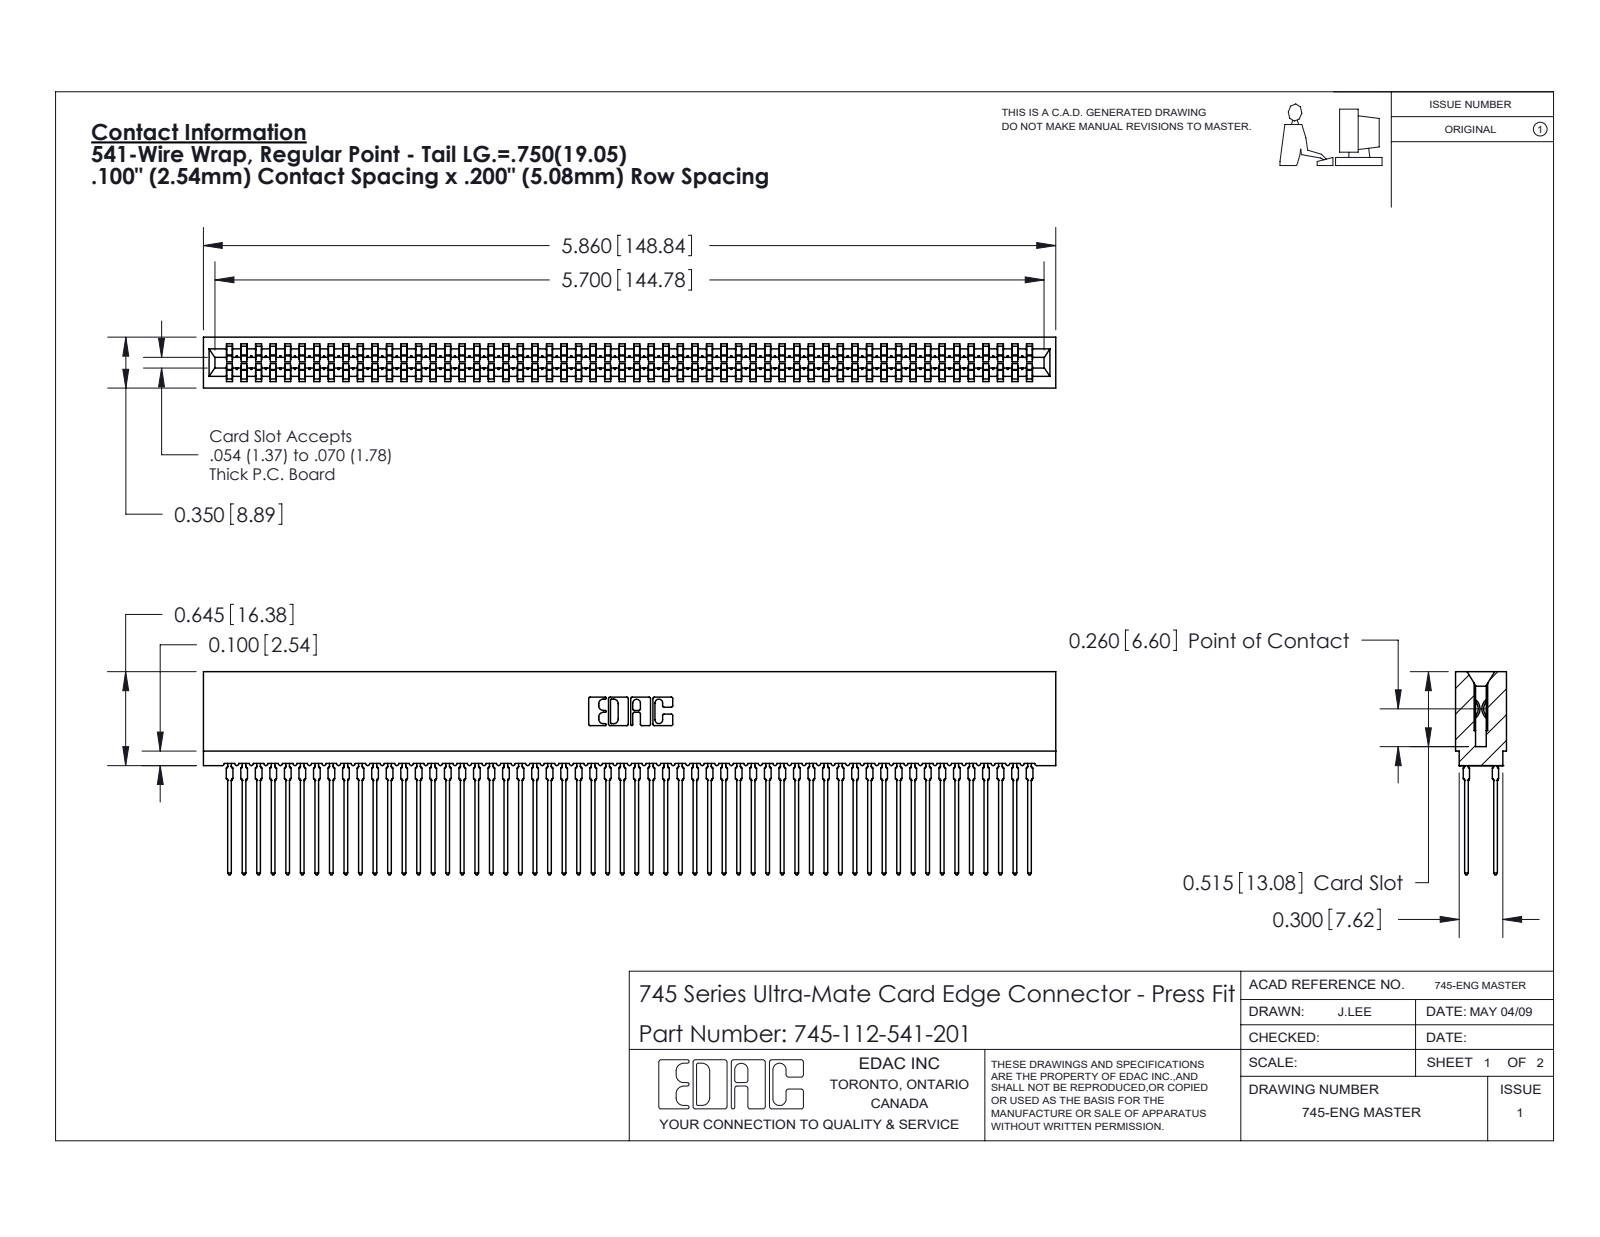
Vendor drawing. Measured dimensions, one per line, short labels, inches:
name: 745-112-541-201; 745-292-001_541; 745 Part_Insulator Option - 01
written by: SolidWorks 2020 (CONFIG_CONTROL_DESIGN)
unit: in
bodies: 113 solids, 10119 faces (5207 planar, 2000 cylindrical, 2912 other)
size: 5.86 × 1.396 × 0.35
volume: 0.846 in³; area: 47.65 in²
rounds: 224× R0.021, 112× R0.015, 22× R0.01, 8× R0.005, 8× R0.011, 6× R0.007, 6× R0.031, 3× R0.026
face distances: 0.063, 0.287, 0.2, 0.35, 0.087, 0.263, 0.025, 0.045, 0.305, 0.018
